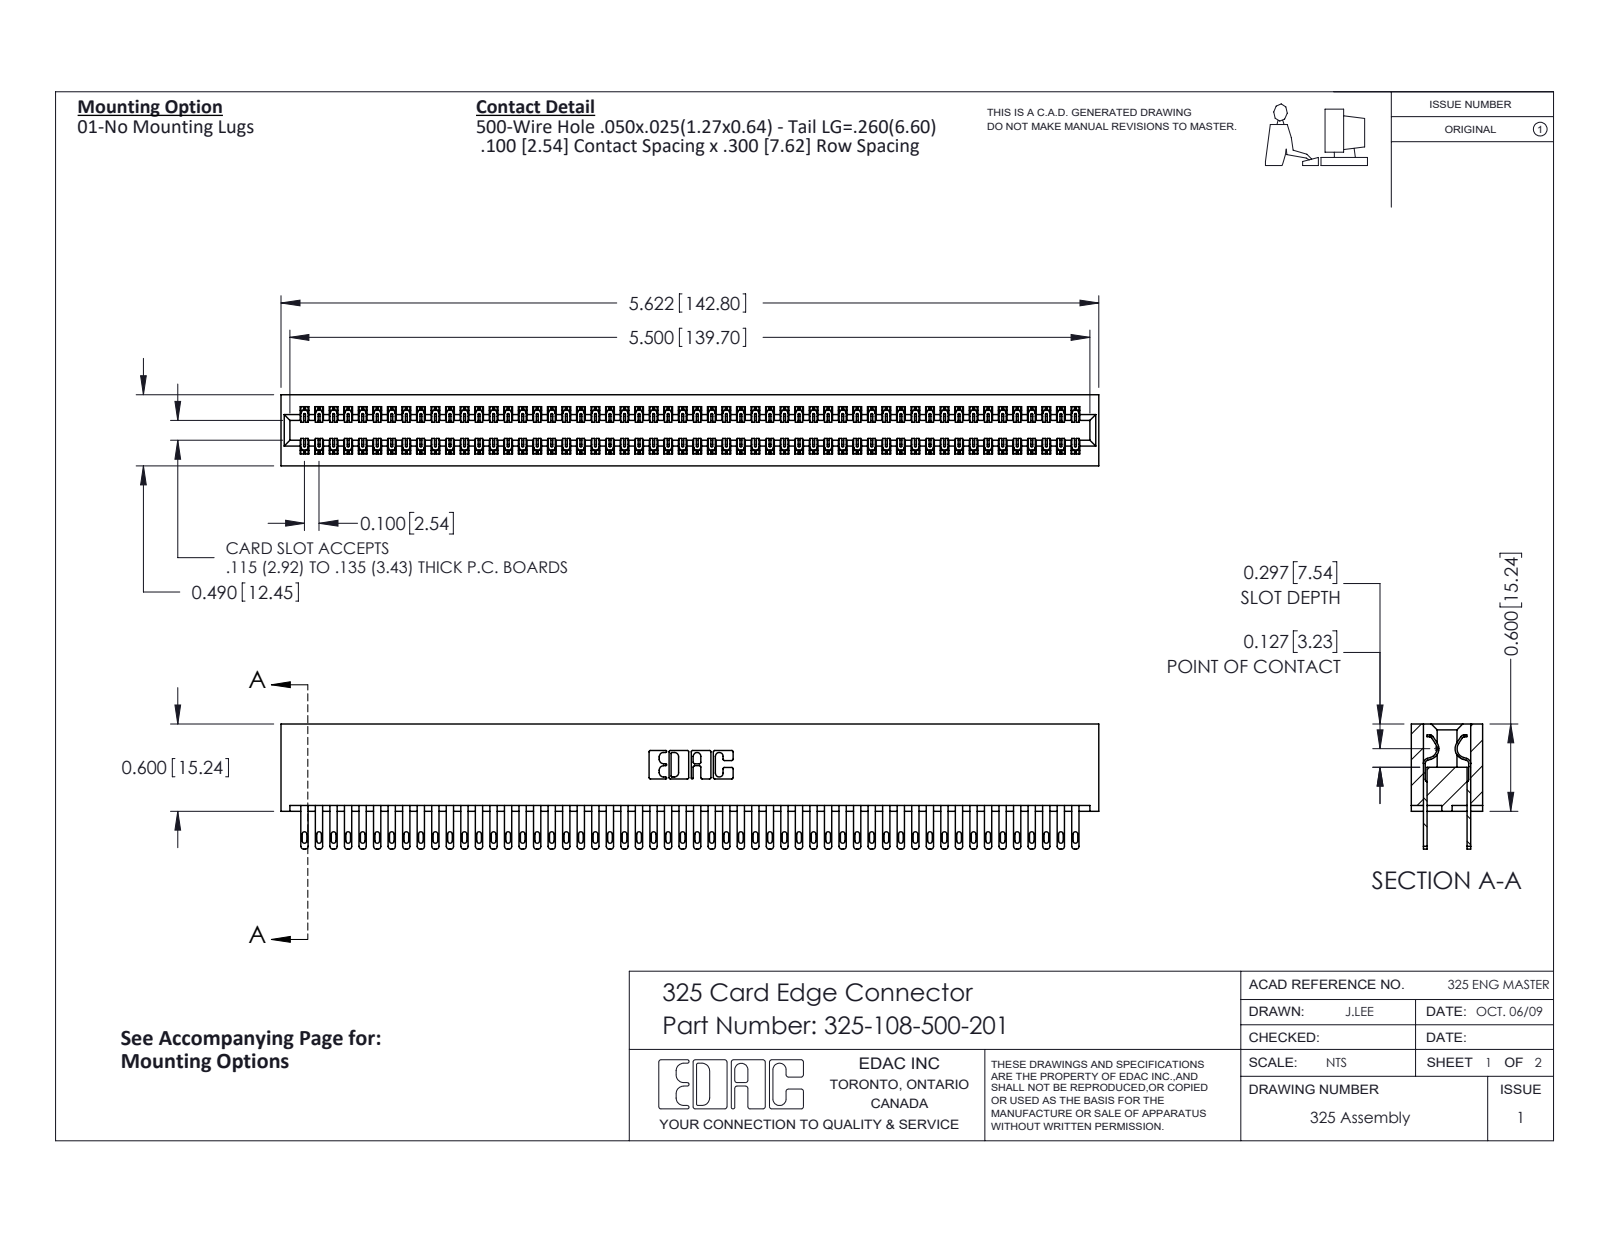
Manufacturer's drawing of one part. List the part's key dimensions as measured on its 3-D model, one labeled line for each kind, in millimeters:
Part name (STEP PRODUCT): 325-108-500-201; 325-292-001_325-293-100; 325 Part_Lugless
STEP written by: SolidWorks 2016 (CONFIG_CONTROL_DESIGN)
Units: millimetres
Bodies: 109 solids, 5290 faces (3306 planar, 1984 cylindrical, 0 other)
Overall size (bounding box): 142.8 × 21.8 × 12.4
Volume: 19 480 mm³ · Surface area: 25 650 mm²
Partial cylindrical surfaces — rounded edges, fillets, slot ends (radius × count): R0.2 ×162, R0.4 ×108, R0.5 ×108, R0.3 ×22, R0.2 ×6, R0.8 ×6, R0.7 ×3, R0.4 ×2
Main face-to-face distances: 2.1, 10.3, 7.6, 2.7, 9.7, 0.6, 8.3, 12.4, 7, 14.2
